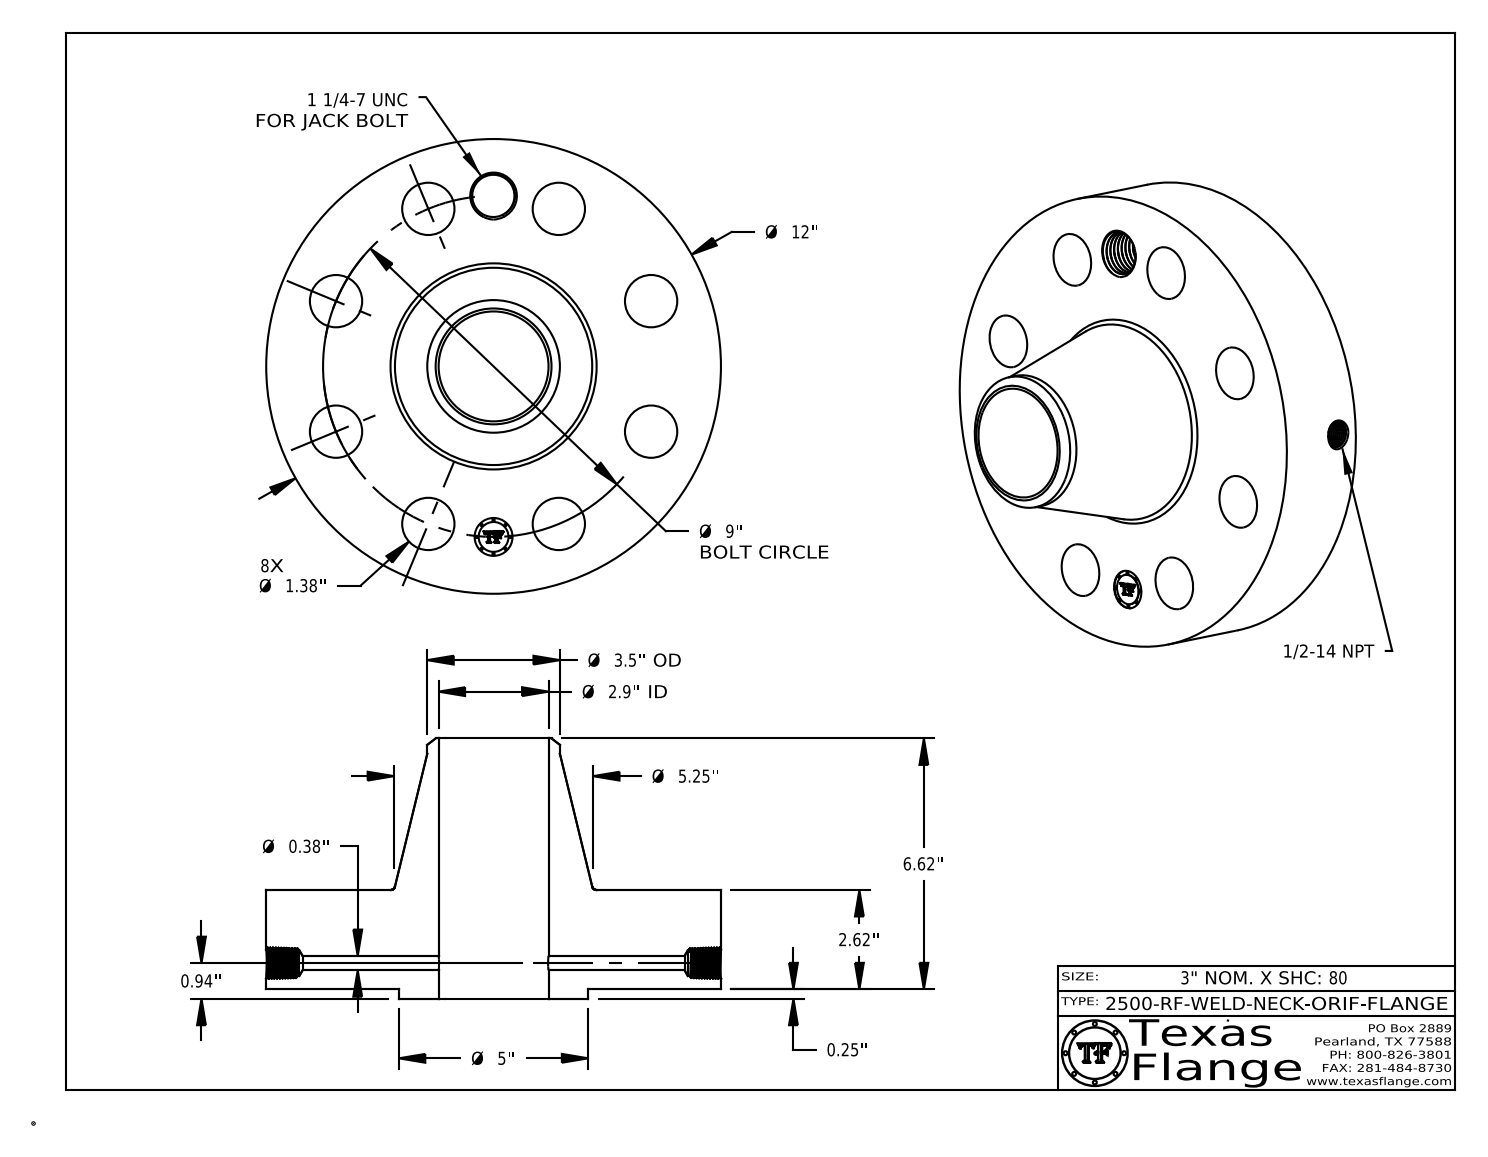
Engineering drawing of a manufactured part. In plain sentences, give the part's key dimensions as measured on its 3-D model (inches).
The part is named "2500-RF-WELD-NECK". Its 3-D file was written by "CATIA V5 STEP AP214 (AUTOMOTIVE_DESIGN)". It is 1 solid with 790 faces: 369 planar, 100 cylindrical and 321 other. Overall it measures 12 by 12 by 6.87 inches. Its volume is 278.5 cubic inches and its surface area 513.4 square inches. Round holes: 8 of diameter 1.38, 1 of diameter 0.375, 1 of diameter 0.672, 1 of diameter 1, 1 of diameter 1.109, 1 of diameter 2.9. Round bosses or shafts: 8 of diameter 0.061, 1 of diameter 12, 1 of diameter 5, 1 of diameter 3.5, 1 of diameter 0.788. The main face-to-face distances are 2.62, 0.25, 2.87, 6.87, 6.62, 4, 2.855, 2.605, 0.015, 4.015. The hole center spacings are 4.5, 3.444, 6.364, 8.315, 9, 1.756, 5, 7.483.
